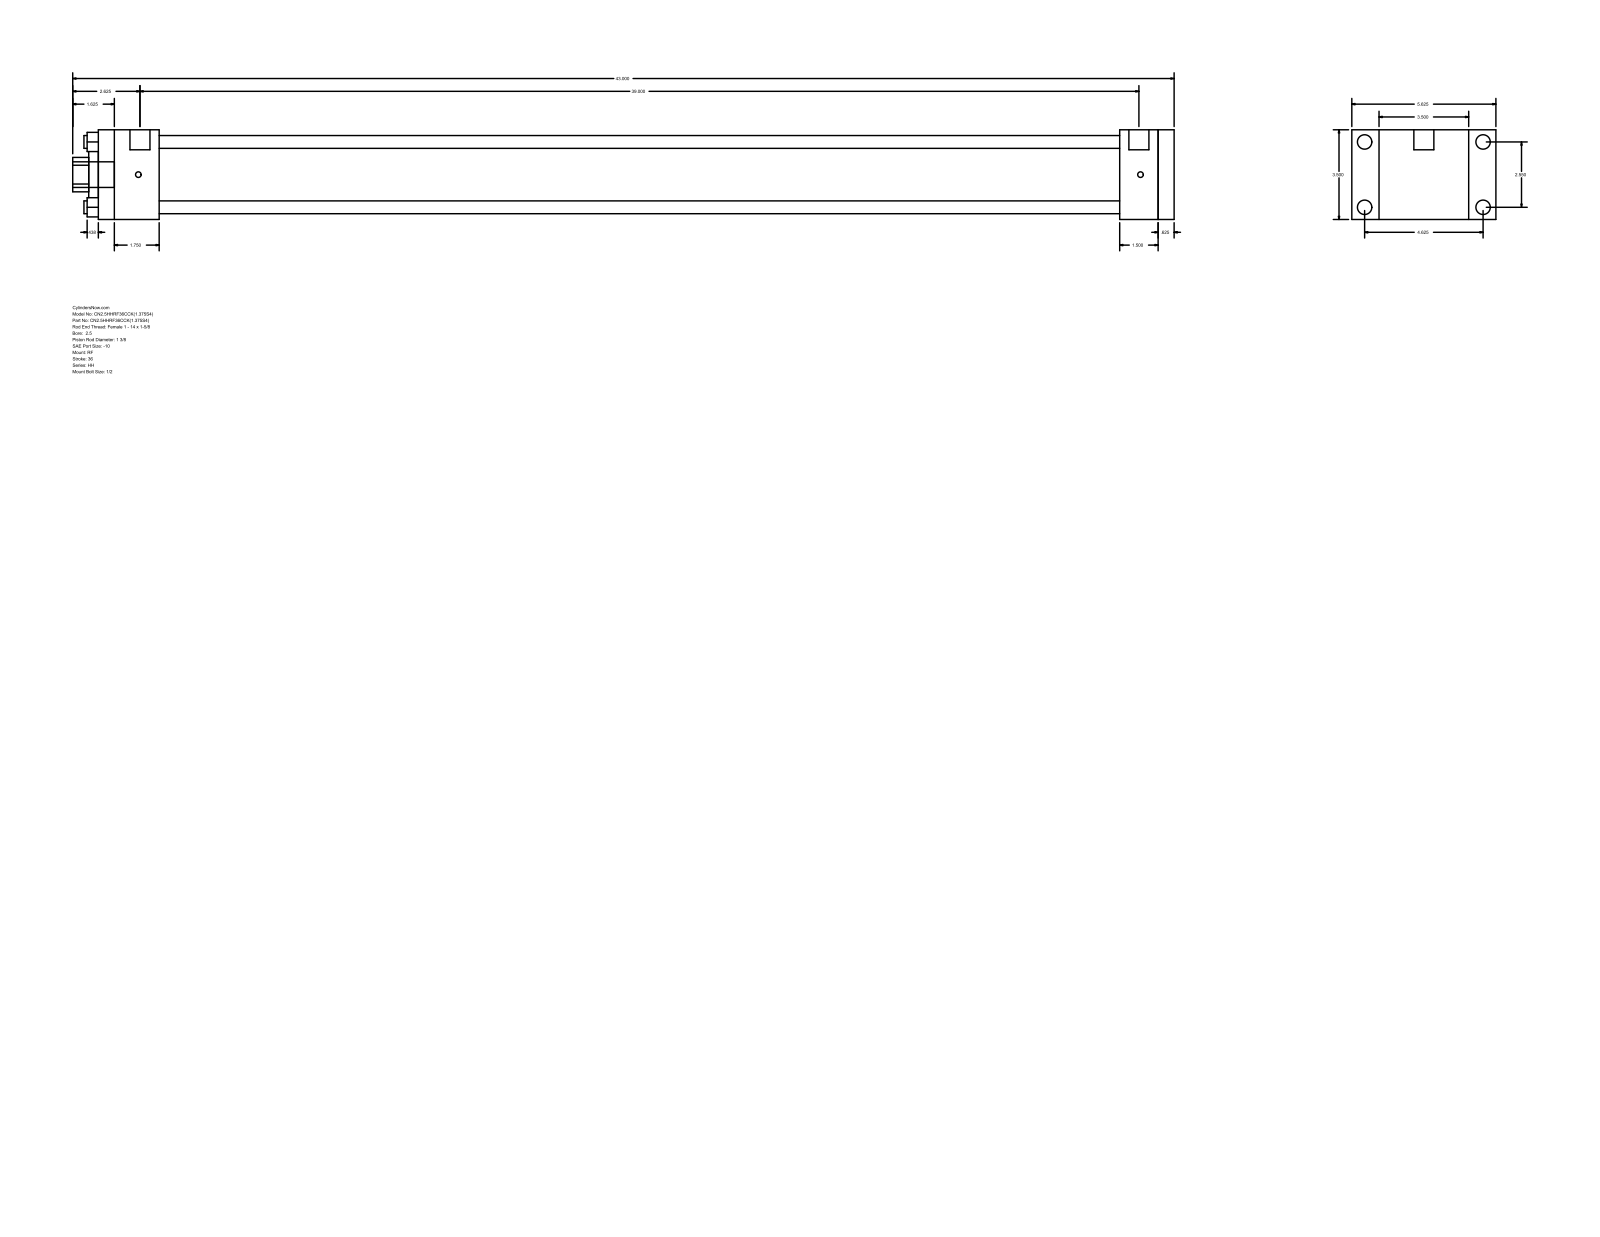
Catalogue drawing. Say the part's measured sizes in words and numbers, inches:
The part is named "HH_RF__0250_1.375". Its 3-D file was written by "GSSL Pune (CONFIG_CONTROL_DESIGN)". It is 0 solids with 92 faces: 64 planar, 28 cylindrical and 0 other. Overall it measures 43 by 5.625 by 3.5 inches. Round holes: 4 of diameter 0.5, 1 of diameter 1.375, 1 of diameter 2, 1 of diameter 2.875. Round bosses or shafts: 4 of diameter 0.563, 4 of diameter 0.219, 2 of diameter 0.781, 1 of diameter 1. Partial cylindrical surfaces (rounded edges, fillets, slot ends): 1 of radius 0.672. The main face-to-face distances are 3.5, 0.625, 41.375, 42, 2.375, 39, 39.625, 39.875, 37.5, 1.5. The hole center spacings are 1.803, 2.55, 3.606.
